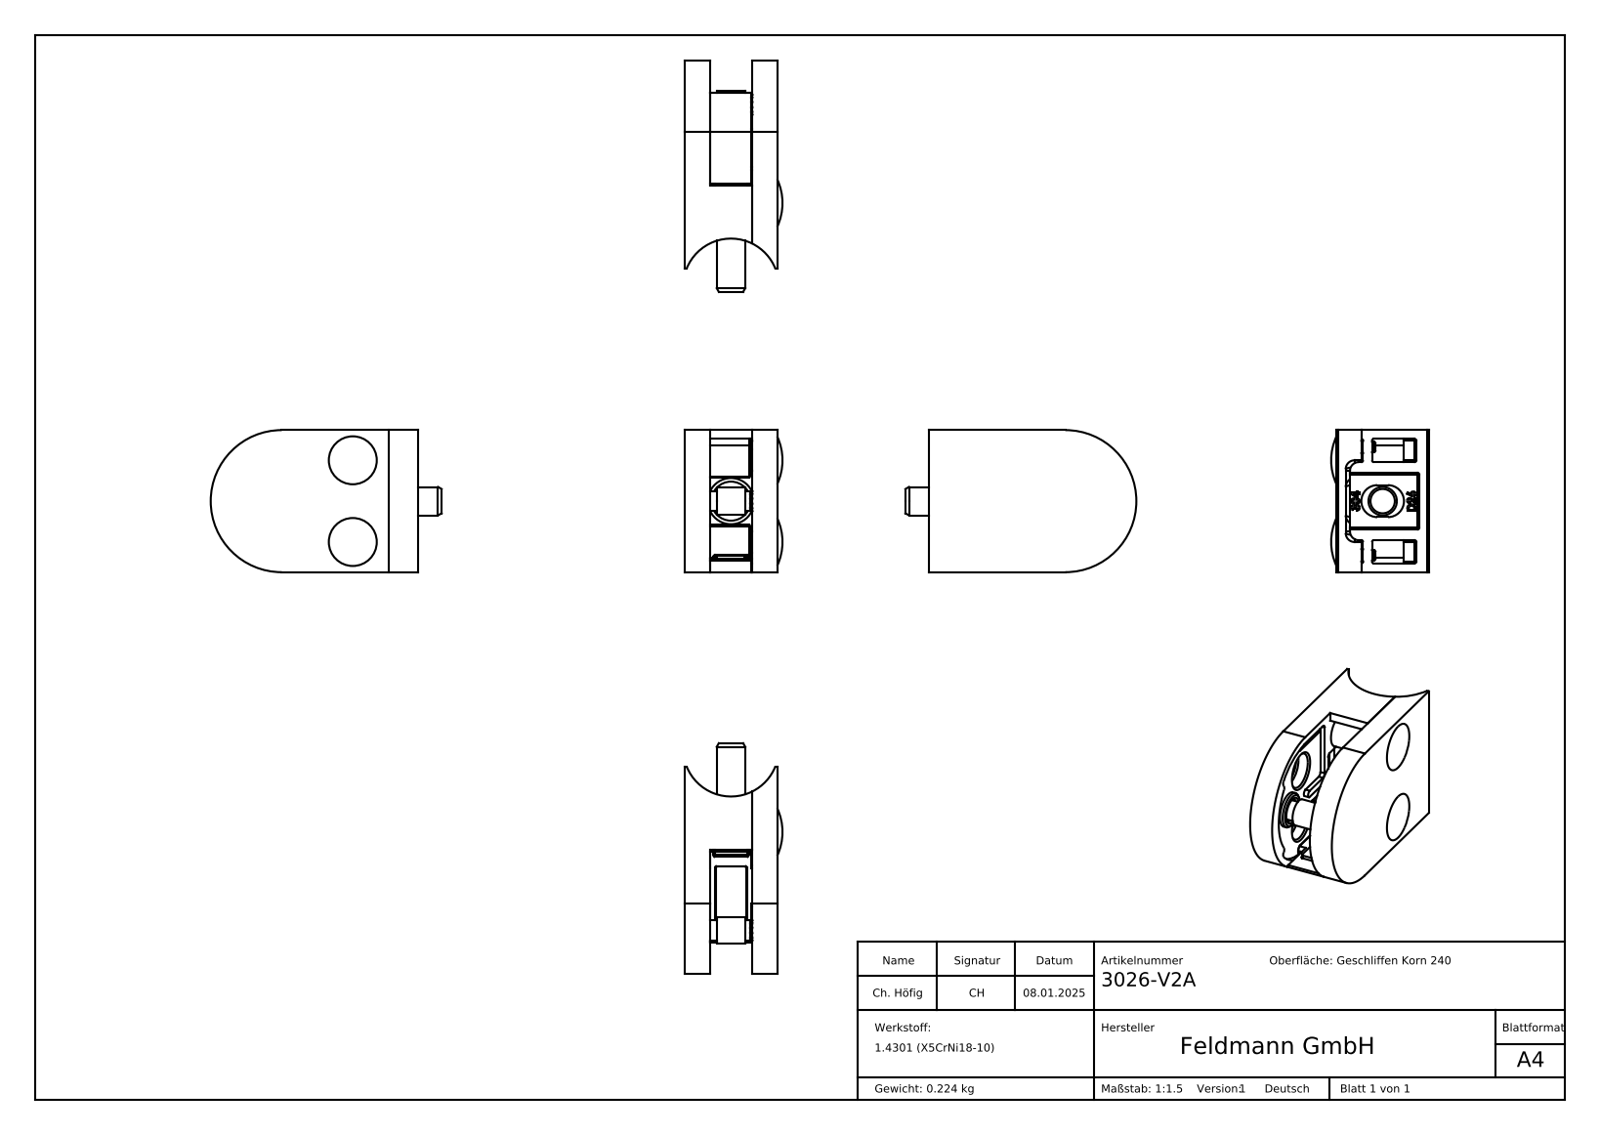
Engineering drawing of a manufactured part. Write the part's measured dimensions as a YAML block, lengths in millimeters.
part_name: "DIN 912 Konfig_DIN 912 M8x20; 3026-V2A; 30xx-XXX Teil1_3026-V2A Teil1; 30-STIFT Teil1_30-STIFT Teil1 (+8 more)"
step_written_by: "SolidWorks 2018 (CONFIG_CONTROL_DESIGN)"
units: millimeters
bodies: {solids: 11, faces: 1804, planar: 962, cylindrical: 181, other: 661}
overall_size: [65, 40, 27.5]
volume: 28970
surface_area: 20674
round_holes:
  - {diameter: 6.5, count: 3}
  - {diameter: 2, count: 2}
  - {diameter: 5, count: 2}
  - {diameter: 10, count: 2}
  - {diameter: 12.5, count: 2}
  - {diameter: 5.6, count: 1}
round_bosses_or_shafts:
  - {diameter: 6, count: 3}
  - {diameter: 12, count: 2}
  - {diameter: 13, count: 1}
  - {diameter: 10, count: 1}
  - {diameter: 8, count: 1}
  - {diameter: 7.6, count: 1}
partial_cylinders:
  - {radius: 0.5, count: 71}
  - {radius: 1, count: 20}
  - {radius: 2.5, count: 11}
  - {radius: 2, count: 6}
  - {radius: 4.5, count: 4}
  - {radius: 0.75, count: 2}
  - {radius: 0.3, count: 1}
  - {radius: 13.45, count: 1}
face_to_face_distances: [26, 19, 7, 1.35, 5.65, 20.35, 13.35, 40, 12, 2]
hole_center_spacings: [11.47, 20.22, 28.28, 29.99, 17, 23]
